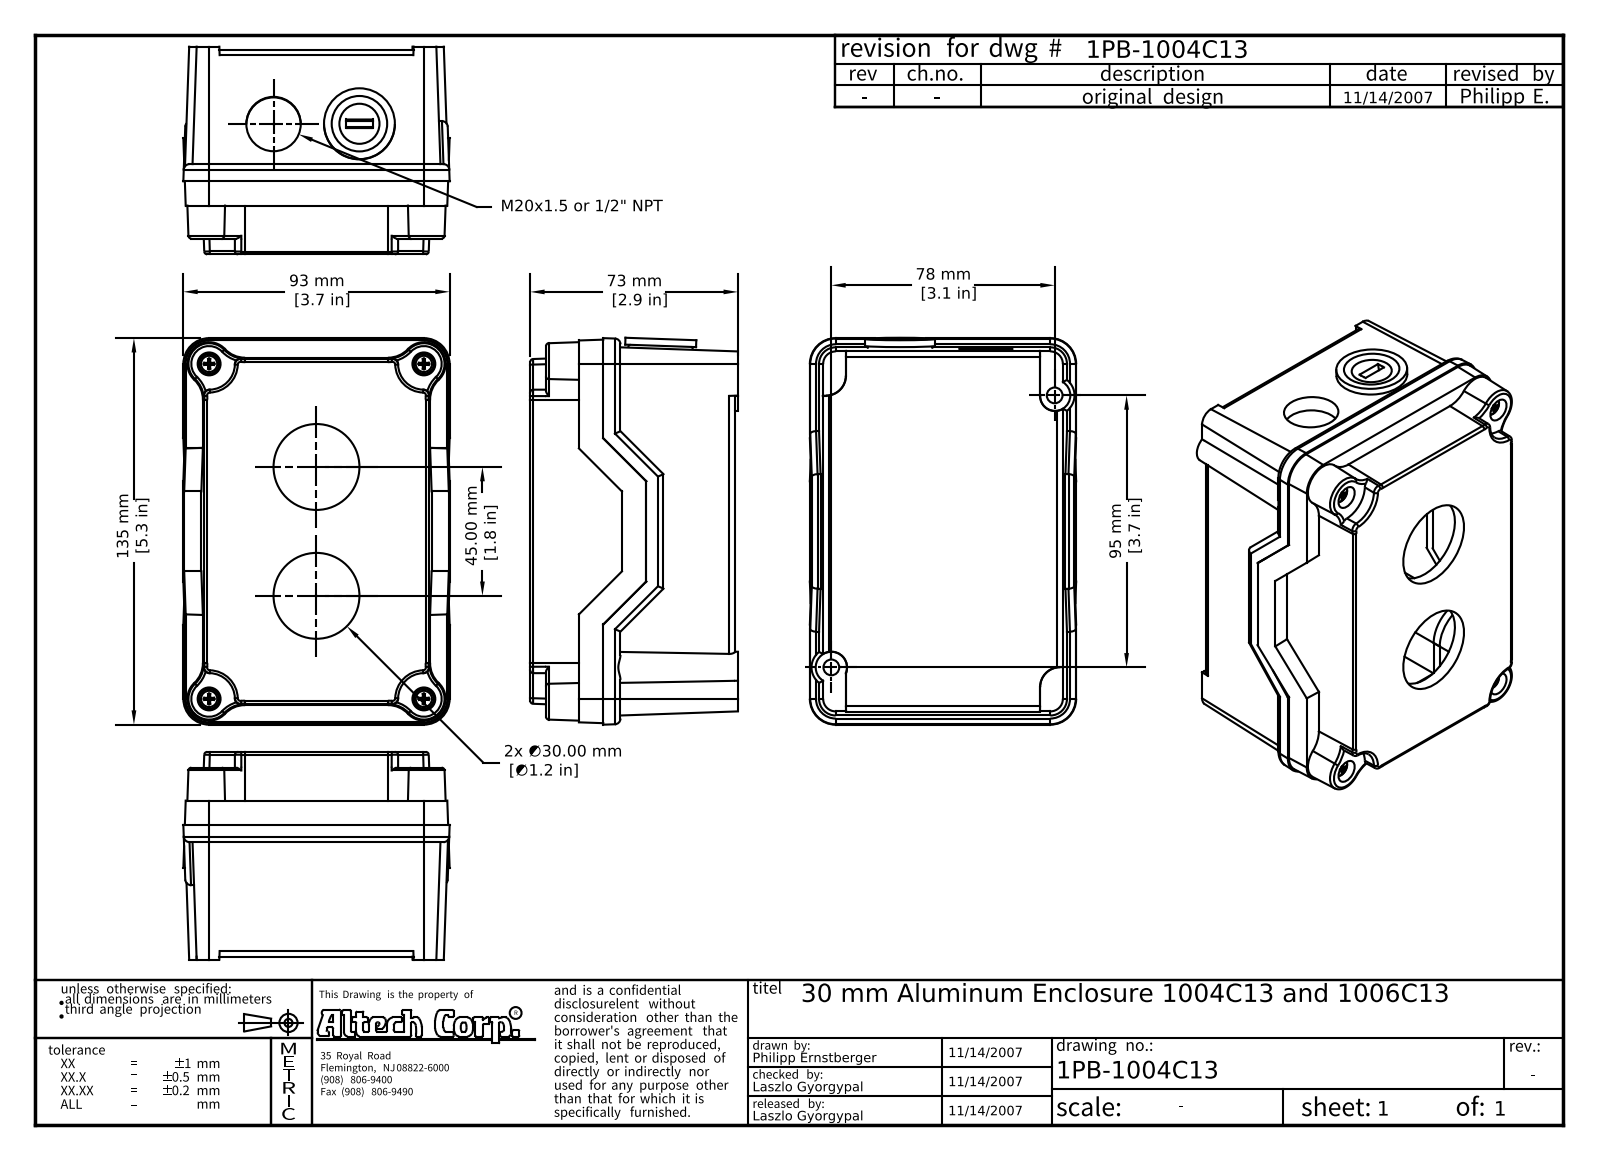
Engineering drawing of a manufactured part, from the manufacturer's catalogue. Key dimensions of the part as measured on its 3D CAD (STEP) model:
Part name (STEP PRODUCT): 1004C13; enclosure_back; enclosure_front; ISO 7045 Z M4 x 5 - 4.8 - Z (+4 more)
STEP written by: Autodesk Inventor 2008 (AUTOMOTIVE_DESIGN)
Units: millimetres
Bodies: 12 solids, 504 faces (204 planar, 67 cylindrical, 233 other)
Overall size (bounding box): 135.13 × 93 × 72.5
Volume: 285 974 mm³ · Surface area: 110 215 mm²
Round holes (diameter × count): ⌀3.5 ×4, ⌀4.3 ×2, ⌀19 ×2, ⌀30 ×2
Round bosses / shafts (diameter × count): ⌀3.18 ×4, ⌀9 ×2, ⌀4 ×2, ⌀3.62 ×2, ⌀24.75 ×1
Partial cylindrical surfaces — rounded edges, fillets, slot ends (radius × count): R2 ×14, R9 ×6, R1 ×4, R6 ×2, R8.5 ×2, R11.5 ×2, R12 ×2, R7.75 ×1
Main face-to-face distances: 6, 65.5, 71.5, 67, 4.5, 61, 40, 21, 46, 25.5
Hole centre spacings: 51.98, 89.26, 30.51, 33.51, 60.59, 75, 76.69, 86.94
